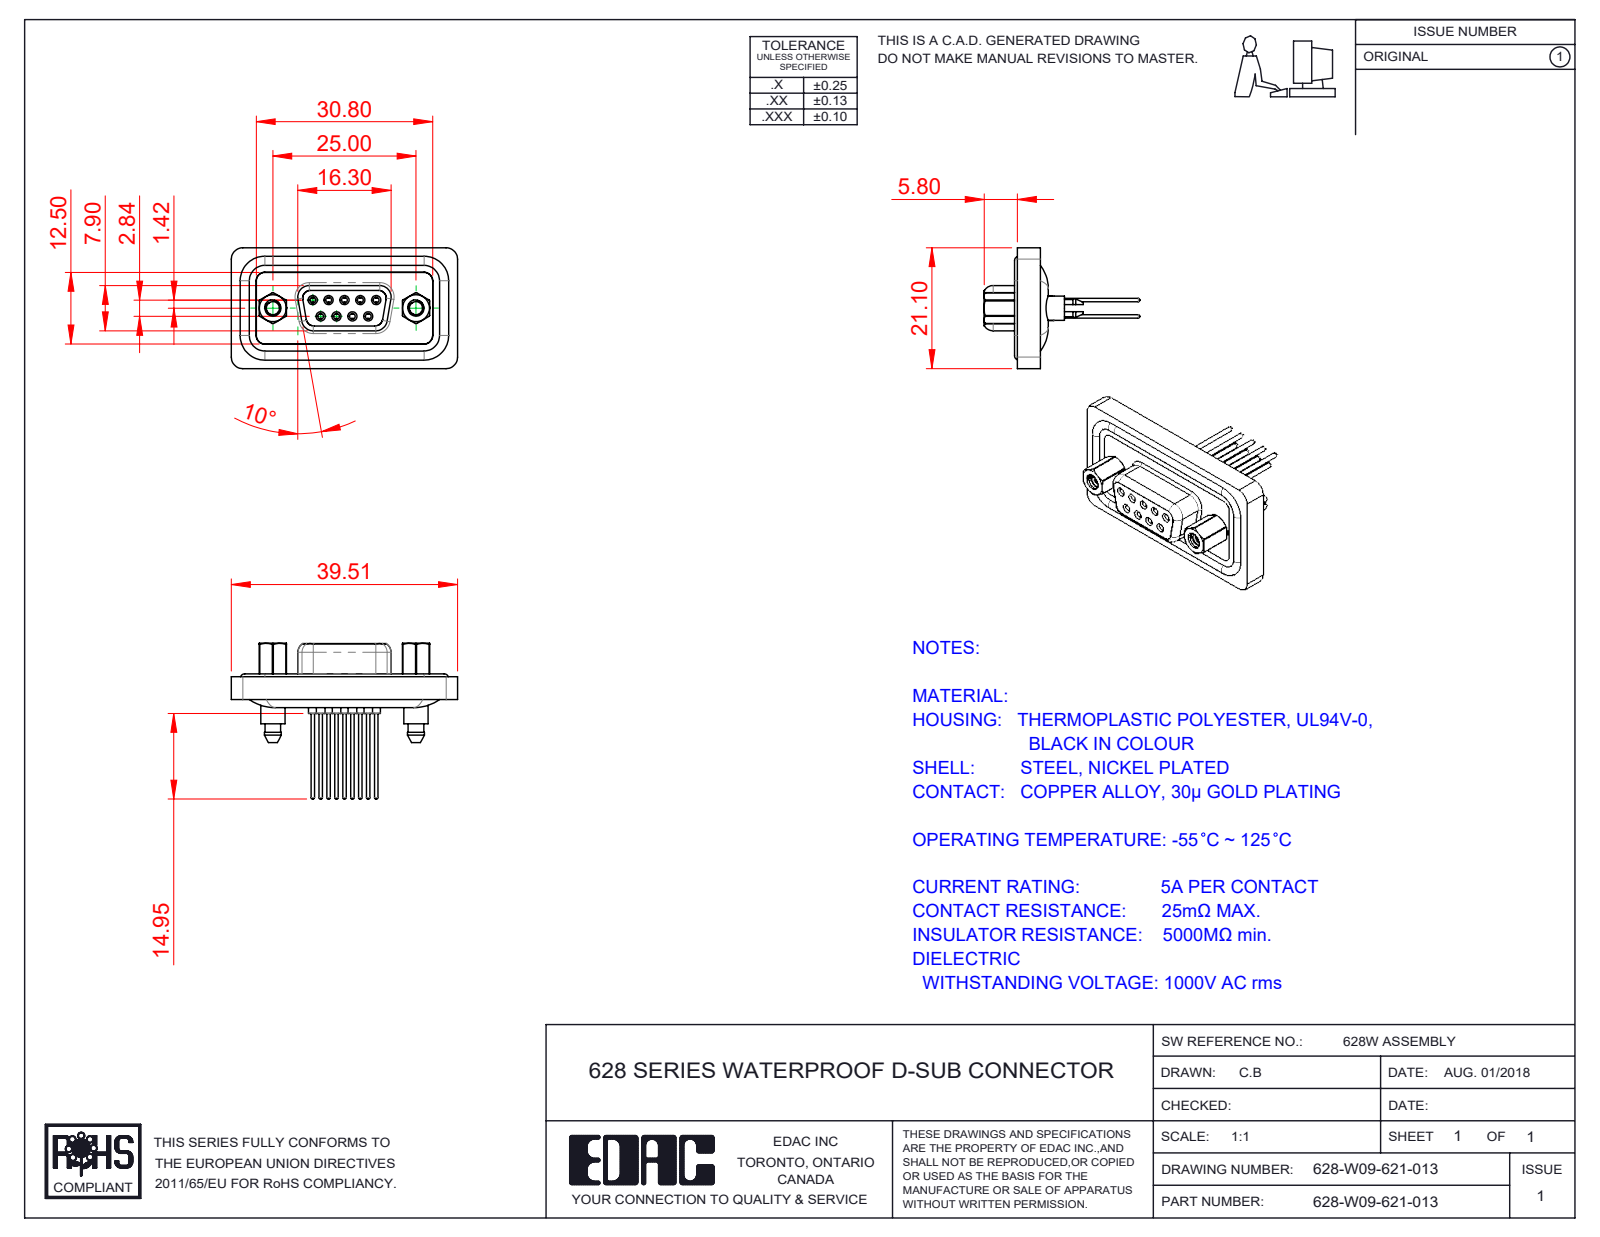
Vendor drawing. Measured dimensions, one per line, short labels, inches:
name: 628W Housing_09 Contacts; 628W Waterproof Housing_09 Contacts BL; 628W Contact Row 2_21; 628W Contact Row 1_21 (+4 more)
written by: SolidWorks 2020 (CONFIG_CONTROL_DESIGN)
unit: in
bodies: 17 solids, 982 faces (250 planar, 437 cylindrical, 295 other)
size: 1.556 × 1.071 × 0.831
volume: 0.276 in³; area: 11.95 in²
holes: 9× ⌀0.039, 9× ⌀0.043, 9× ⌀0.059, 9× ⌀0.067, 9× ⌀0.071, 9× ⌀0.079, 2× ⌀0.089, 2× ⌀0.09, 2× ⌀0.157, 2× ⌀0.167, 2× ⌀0.189
bosses: 13× ⌀0.063, 9× ⌀0.087, 9× ⌀0.024, 4× ⌀0.059, 2× ⌀0.213, 2× ⌀0.193, 2× ⌀0.11, 1× ⌀0.189
rounds: 16× R0.059, 14× R0.079, 8× R0.053, 6× R0.063, 4× R0.02, 4× R0.035, 4× R0.069, 4× R0.106
face distances: 0.016, 0.063, 0.114, 0.043, 0.071, 0.098, 0.142, 0.157, 0.028, 0.02
hole spacings: 0.124, 0.109, 0.218, 0.198, 0.198, 0.294, 0.295, 0.327
